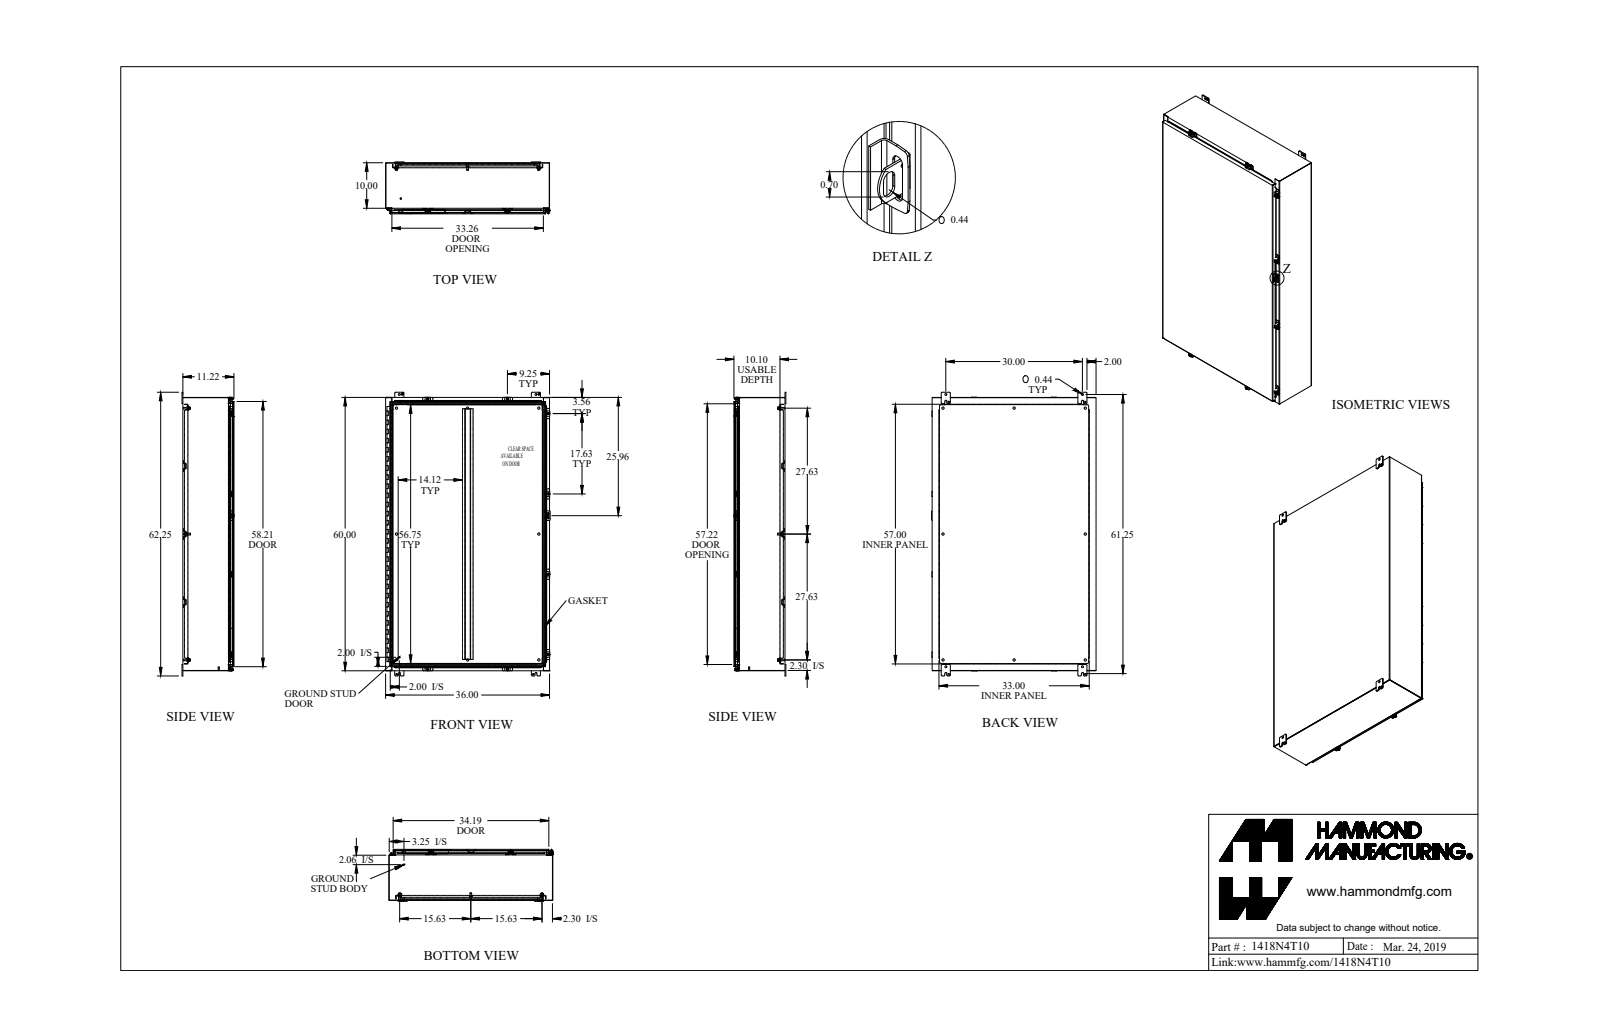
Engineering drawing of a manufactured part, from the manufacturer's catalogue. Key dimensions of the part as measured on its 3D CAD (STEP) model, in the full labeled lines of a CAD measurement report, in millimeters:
Part name (STEP PRODUCT): 1418N4T10_Default
STEP written by: SolidWorks 2019 (CONFIG_CONTROL_DESIGN)
Units: millimetres
Bodies: 69 solids, 2458 faces (1445 planar, 913 cylindrical, 100 other)
Overall size (bounding box): 1581.2 × 917.6 × 290.5
Volume: 12 080 000 mm³ · Surface area: 12 390 000 mm²
Round holes (diameter × count): ⌀5.4 ×8, ⌀6.7 ×8, ⌀9.5 ×8, ⌀12.7 ×8, ⌀7.8 ×4, ⌀8 ×4, ⌀11.1 ×4, ⌀11.3 ×4, ⌀3.2 ×1, ⌀4.7 ×1
Round bosses / shafts (diameter × count): ⌀16.5 ×8, ⌀12.7 ×8, ⌀9.9 ×8, ⌀9.5 ×8, ⌀8.4 ×8, ⌀6.2 ×8, ⌀25.4 ×4, ⌀7.1 ×2
Partial cylindrical surfaces — rounded edges, fillets, slot ends (radius × count): R6.4 ×44, R1.2 ×39, R3.6 ×39, R4.8 ×36, R0.9 ×22, R2.7 ×22, R2.9 ×16, R3.6 ×16
Main face-to-face distances: 1.8, 283, 281.2, 284.9, 2.4, 256.8, 255, 26.2, 28, 259.2
Hole centre spacings: 182.8, 396.9, 621.5, 1403.4, 1458.4, 701.7, 793.8, 1467.7
